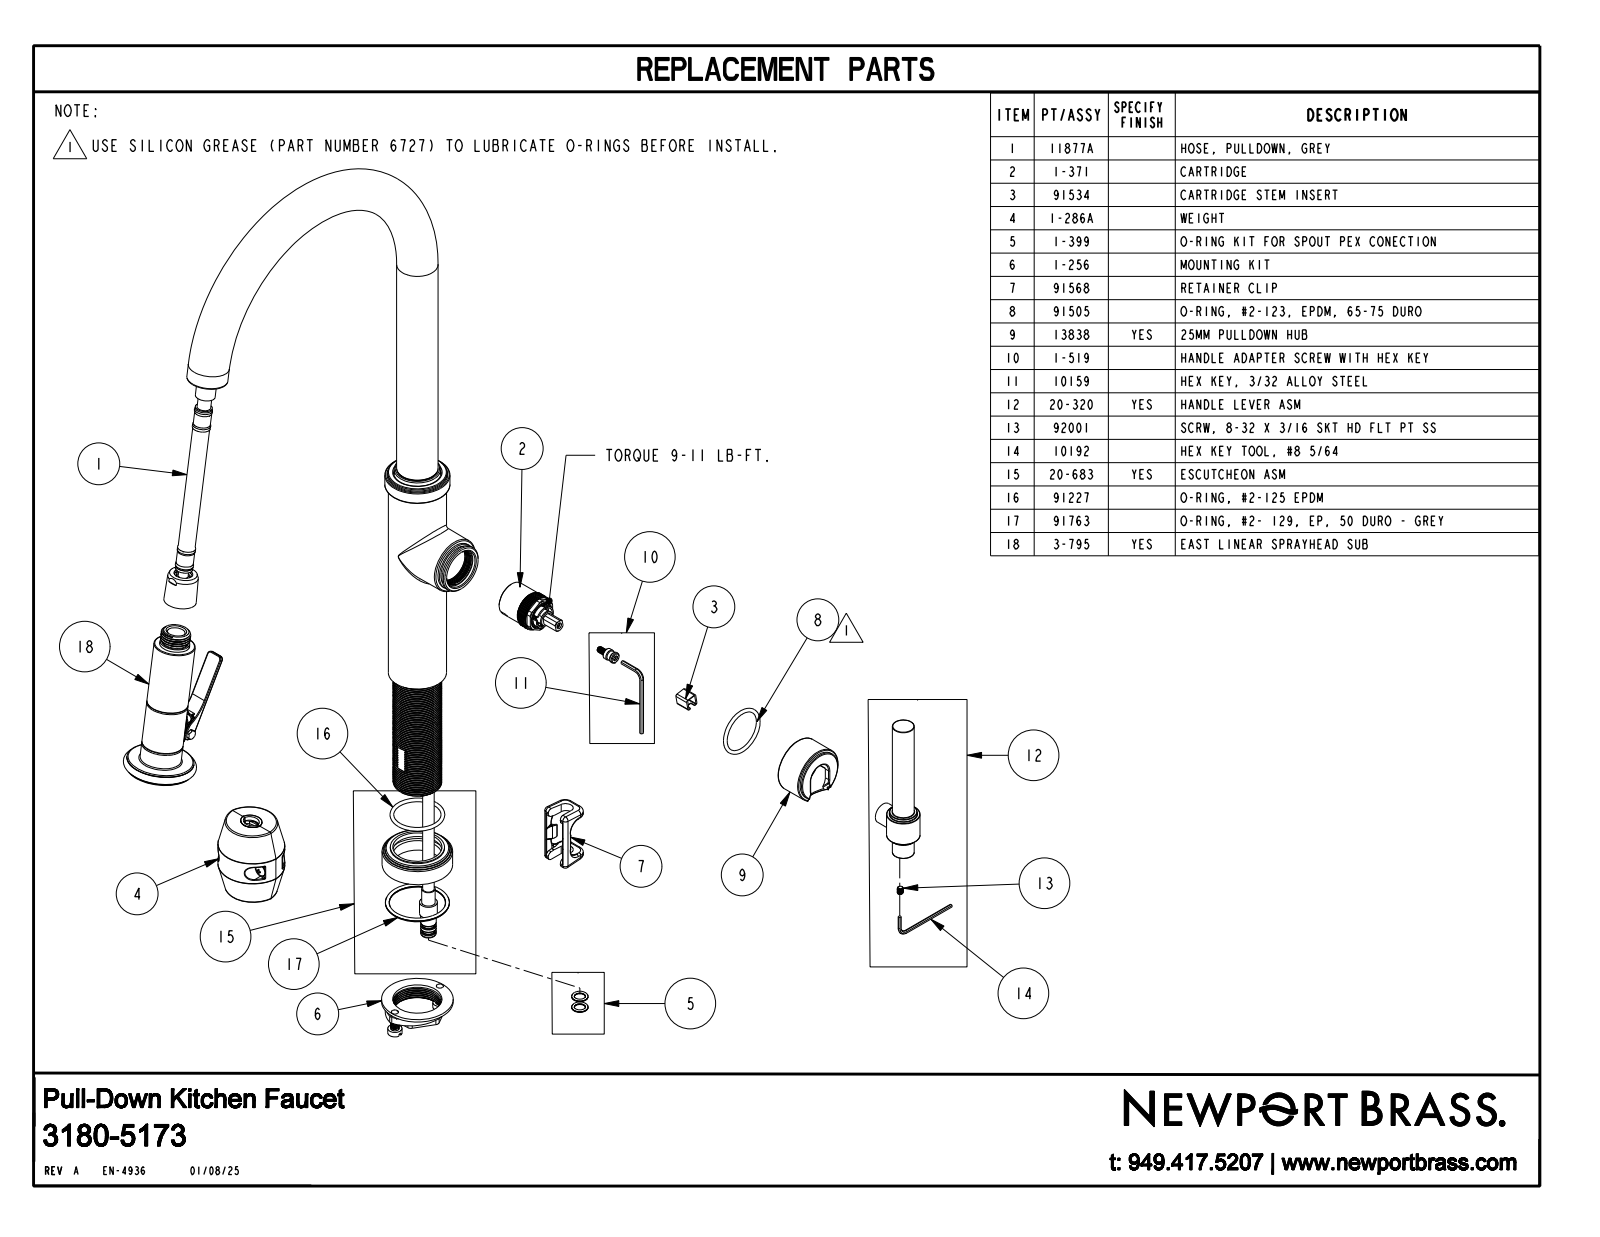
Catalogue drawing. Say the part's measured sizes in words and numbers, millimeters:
The part is named "3180-5143". Its 3-D file was written by "CREO PARAMETRIC BY PTC INC, 2023134 (CONFIG_CONTROL_DESIGN)". It is 1 solid with 1342 faces: 823 planar, 252 cylindrical and 267 other. Overall it measures 480.8 by 272 by 110.1 millimeters. Its volume is 722 300 cubic millimeters and its surface area 105 700 square millimeters. Round holes: 18 of diameter 1, 1 of diameter 4.3, 1 of diameter 5.3, 1 of diameter 12, 1 of diameter 14.2, 1 of diameter 26.3, 1 of diameter 35.4. Round bosses or shafts: 18 of diameter 2.6, 2 of diameter 29, 1 of diameter 49.3, 1 of diameter 47.1, 1 of diameter 45.5, 1 of diameter 45.2, 1 of diameter 41.4, 1 of diameter 40.6. Partial cylindrical surfaces (rounded edges, fillets, slot ends): 26 of radius 0.5, 23 of radius 0.8, 15 of radius 1.5, 7 of radius 0.6, 4 of radius 1.1, 3 of radius 2.5, 2 of radius 1.7, 2 of radius 5.1. The main face-to-face distances are 7.8, 188.2, 0.4, 188.6, 14, 174.2, 12.7, 3.8, 3.4, 185.2. The hole center spacings are 9.3, 16.2, 17.6, 9.3, 12, 3.3, 6.4, 14.3.
